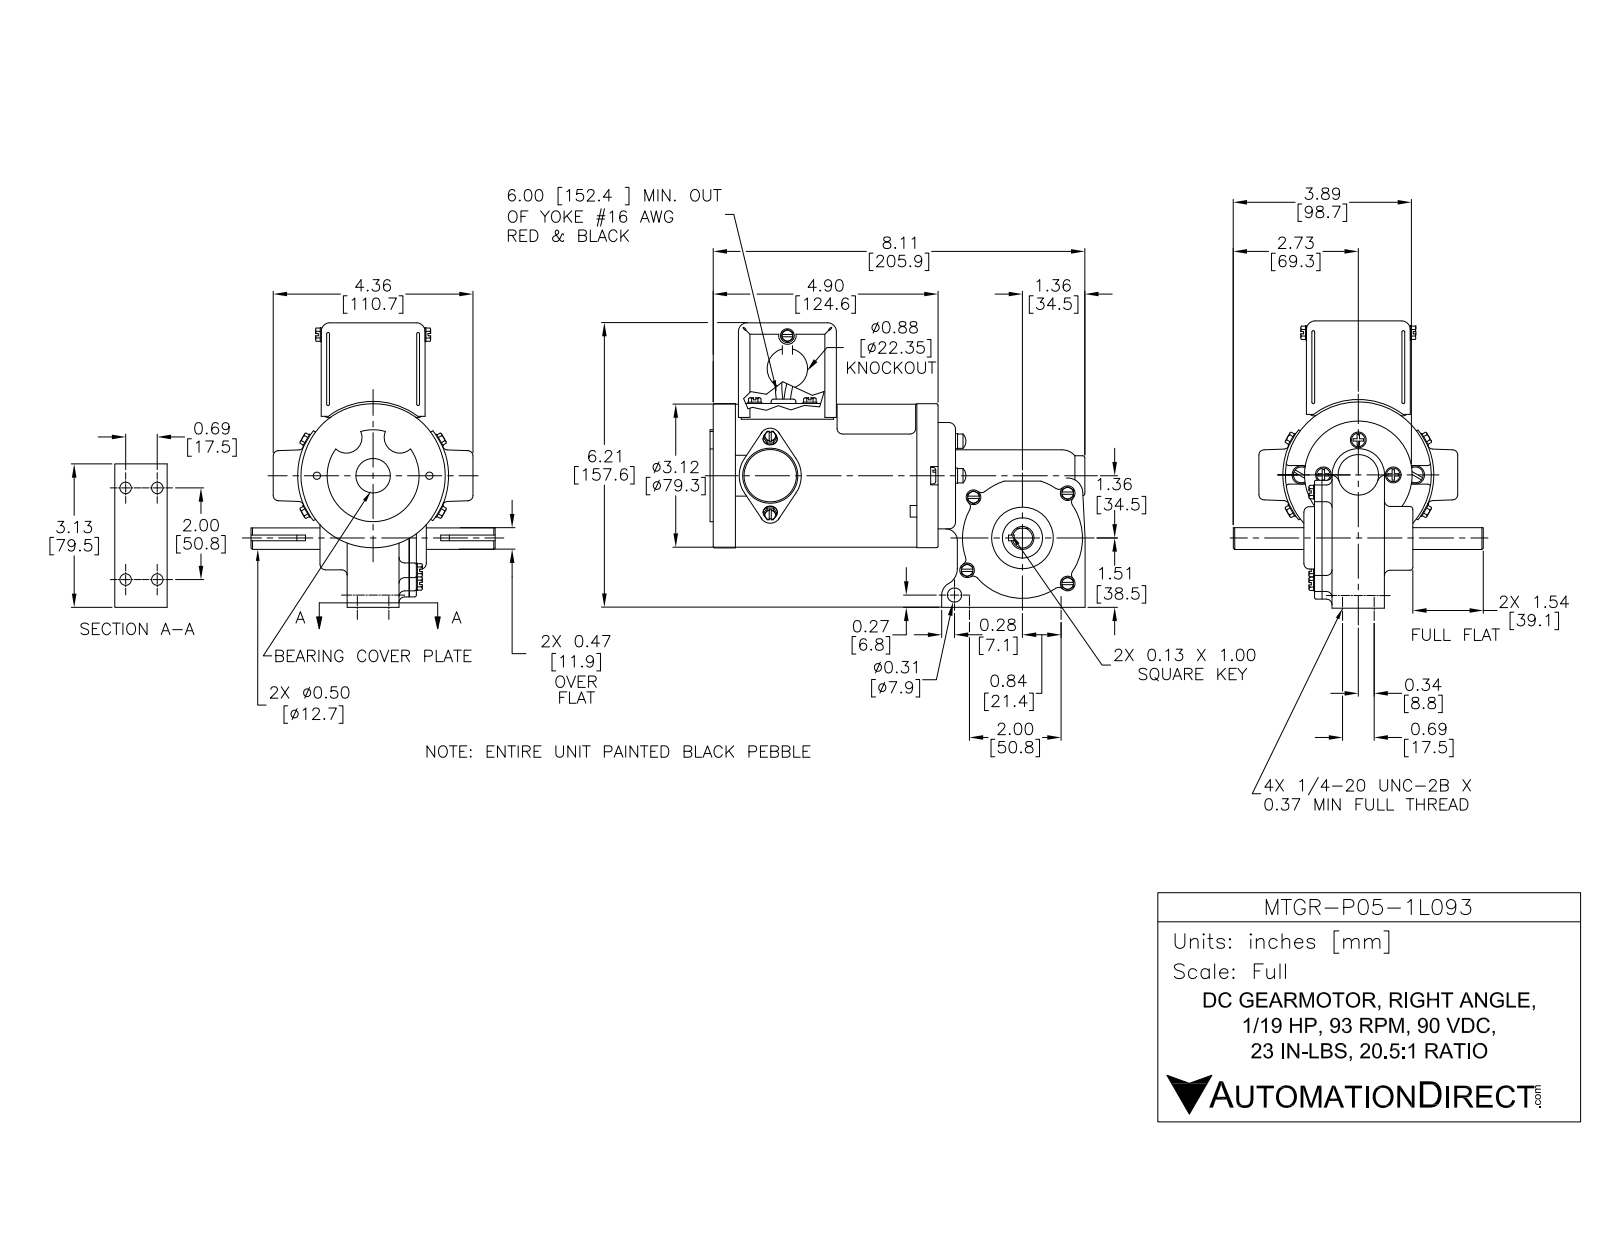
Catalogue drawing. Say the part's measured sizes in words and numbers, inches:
The part is named "P05-1L093". Its 3-D file was written by "SolidWorks 2013 (AUTOMOTIVE_DESIGN)". It is 40 solids with 712 faces: 436 planar, 210 cylindrical and 66 other. Overall it measures 8.179 by 6.274 by 5.453 inches. Its volume is 27.37 cubic inches and its surface area 297.1 square inches. Round holes: 5 of diameter 0.25, 2 of diameter 0.094, 2 of diameter 0.198, 1 of diameter 0.3, 1 of diameter 0.301, 1 of diameter 0.375, 1 of diameter 0.5, 1 of diameter 0.86, 1 of diameter 1.225, 1 of diameter 3, 1 of diameter 3.125. Round bosses or shafts: 4 of diameter 0.321, 4 of diameter 0.3, 3 of diameter 0.346, 3 of diameter 0.295, 2 of diameter 0.125, 2 of diameter 0.1, 1 of diameter 3.156, 1 of diameter 3.14. Partial cylindrical surfaces (rounded edges, fillets, slot ends): 10 of radius 0.1, 4 of radius 0.191, 4 of radius 0.234, 2 of radius 0.15, 2 of radius 0.159, 2 of radius 0.341, 1 of radius 0.25, 1 of radius 0.34. The main face-to-face distances are 0.031, 0.25, 0.063, 4.65, 2.135, 0.307, 2.047, 1.67, 1.608, 0.245. The hole center spacings are 0.343, 0.456, 0.686, 1.23, 2, 2.029, 2.114, 2.326.
